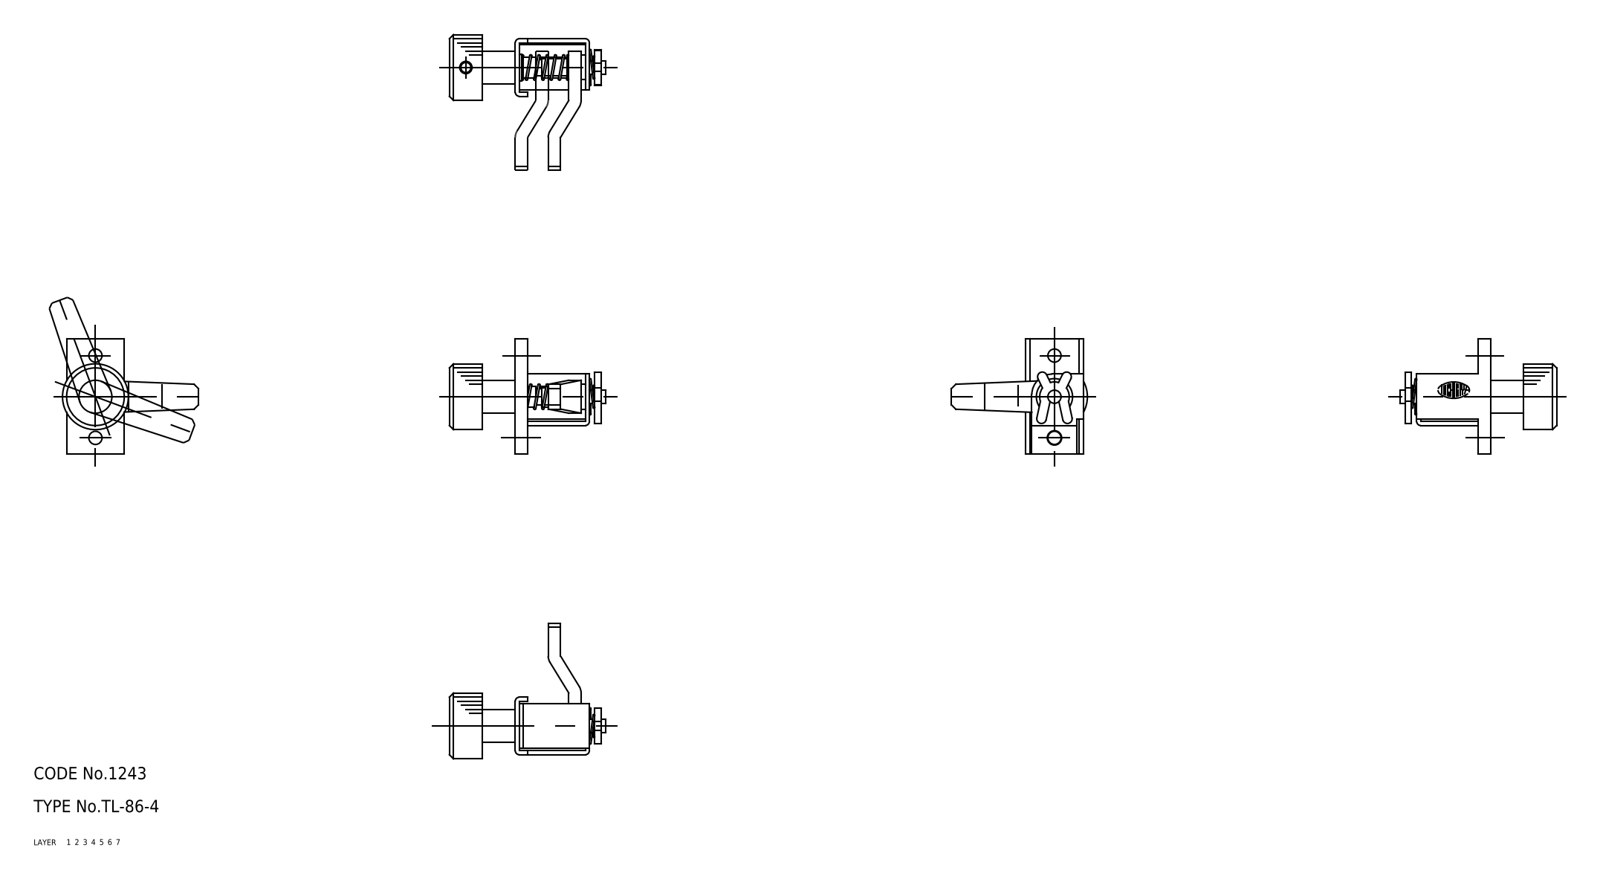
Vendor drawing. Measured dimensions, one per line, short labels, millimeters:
name: spring_2; spring_1; screw; retainer (+6 more)
written by: CADfix (AUTOMOTIVE_DESIGN)
unit: mm
bodies: 9 solids, 193 faces (0 planar, 0 cylindrical, 193 other)
size: 38 × 33 × 28
volume: 4 029 mm³; area: 5 220 mm²
